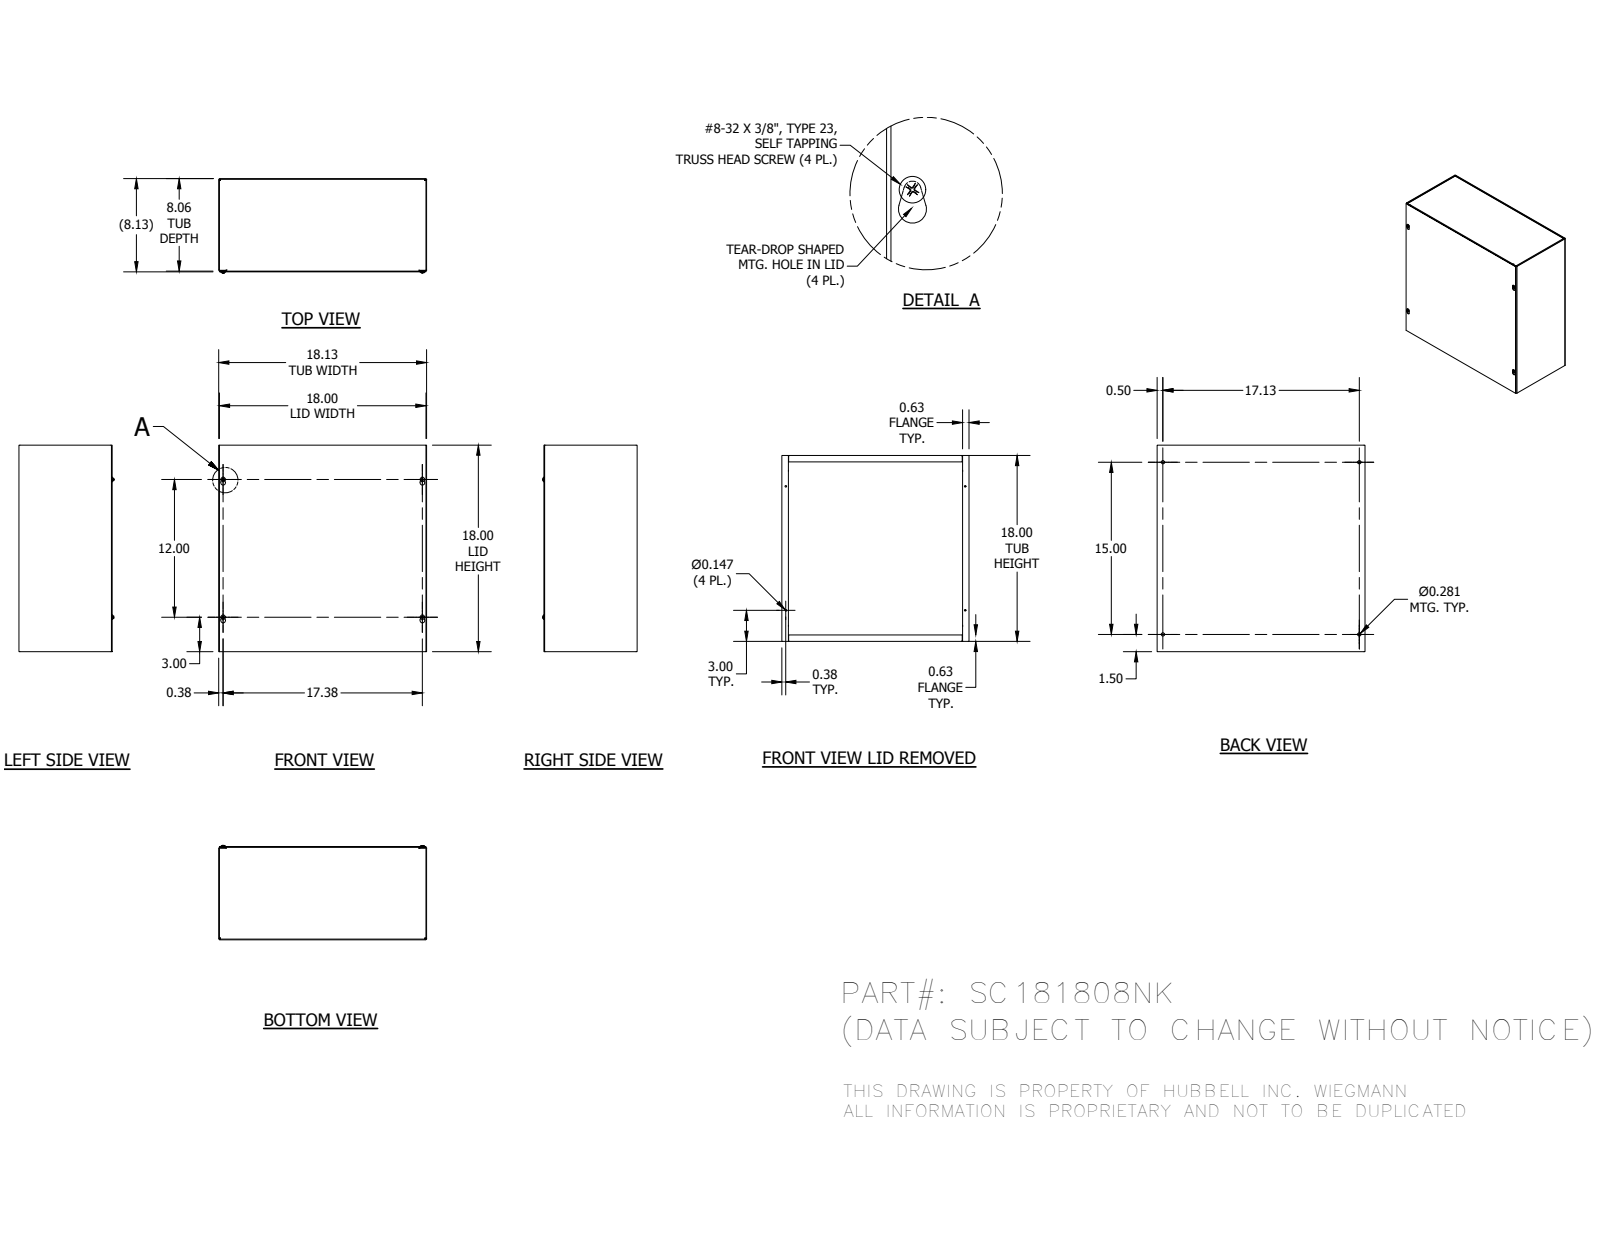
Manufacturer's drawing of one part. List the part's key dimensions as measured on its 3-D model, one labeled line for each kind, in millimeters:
Part name (STEP PRODUCT): SC181808NKBLR; SC1808NKTB; SC1818LPA; 34056 (+1 more)
STEP written by: Autodesk Inventor 2014 (AUTOMOTIVE_DESIGN)
Units: millimetres
Bodies: 8 solids, 268 faces (152 planar, 48 cylindrical, 68 other)
Overall size (bounding box): 460.38 × 457.2 × 208.92
Volume: 1 330 000 mm³ · Surface area: 1 687 000 mm²
Round holes (diameter × count): ⌀3.73 ×4, ⌀7.14 ×4
Round bosses / shafts (diameter × count): ⌀9.75 ×4, ⌀4.17 ×4
Partial cylindrical surfaces — rounded edges, fillets, slot ends (radius × count): R0.79 ×12, R2.38 ×12, R3.17 ×4, R5.16 ×4
Main face-to-face distances: 1.59, 204.79, 203.2, 206.38, 457.2, 455.61, 458.79, 454.02, 460.38, 3.18
Hole centre spacings: 38.23, 342.91, 439.8, 556.38, 304.8, 381, 434.98, 441.32
